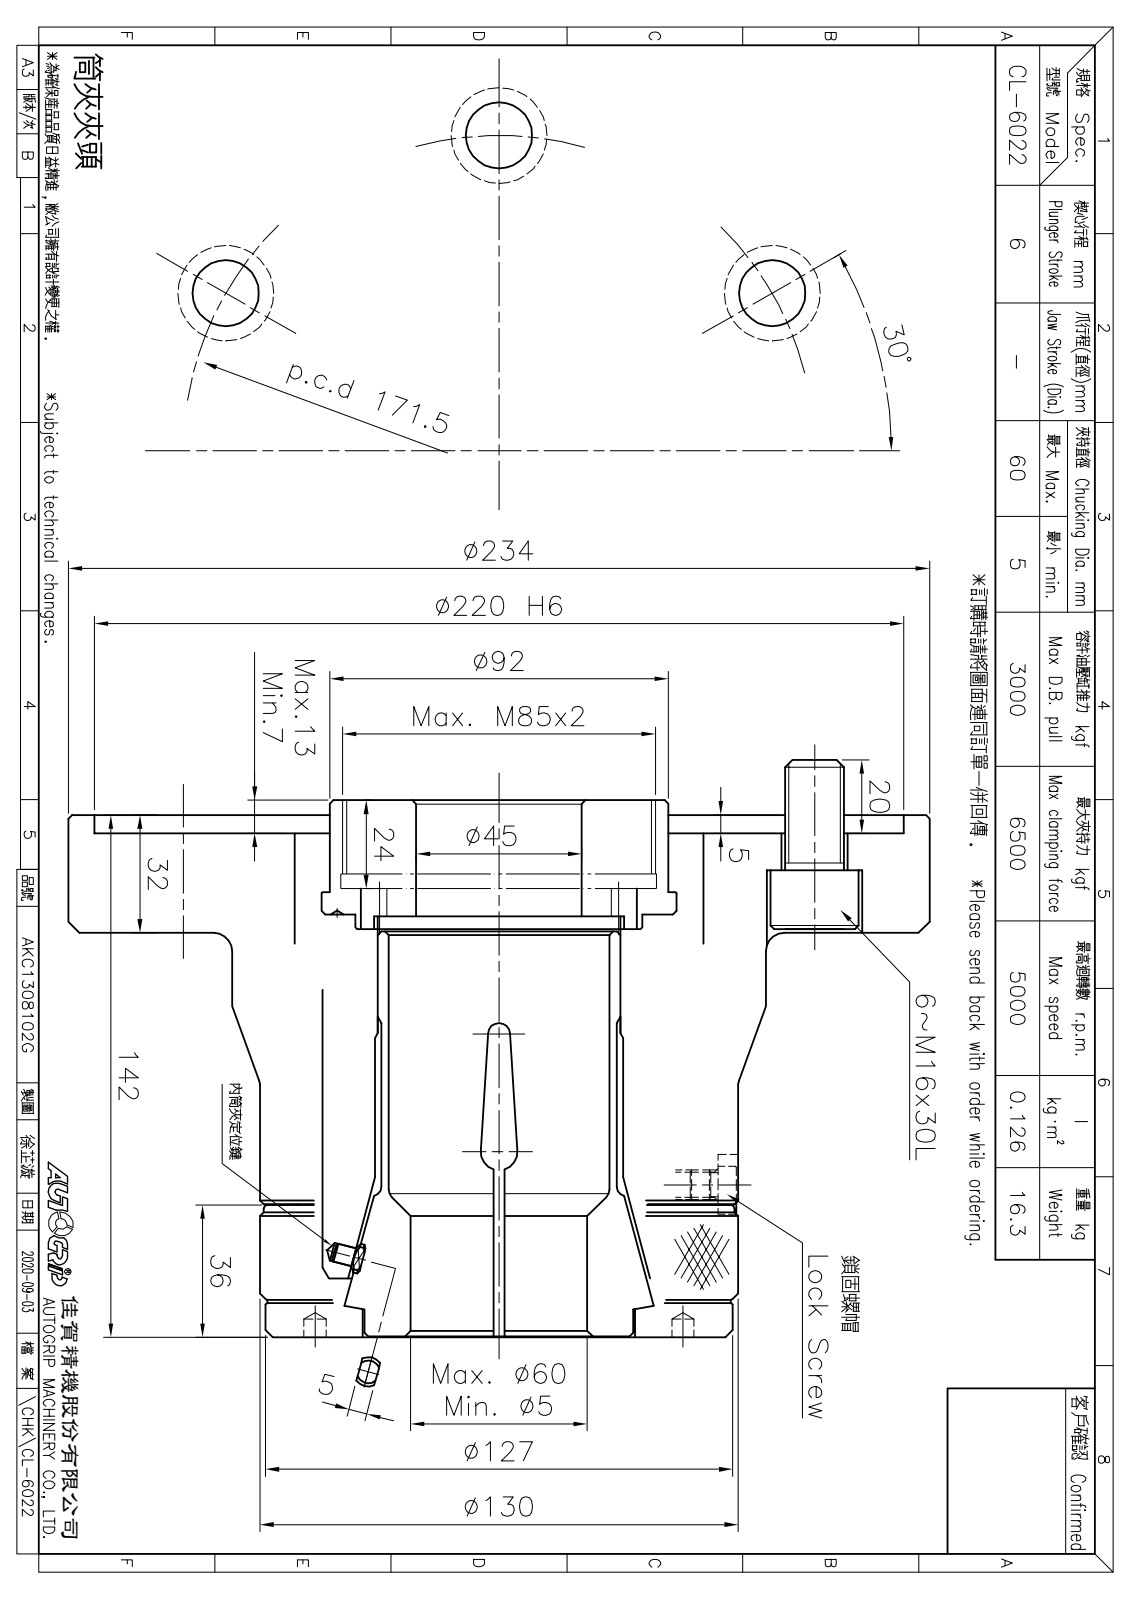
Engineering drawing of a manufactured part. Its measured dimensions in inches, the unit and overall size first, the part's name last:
Units: inches
Overall size (bounding box): 9.213 × 9.213 × 6.173
Round holes (diameter × count): ⌀0.709 ×6, ⌀1.024 ×6, ⌀0.236 ×2, ⌀0.197 ×1, ⌀0.268 ×1, ⌀2.402 ×1, ⌀2.598 ×1, ⌀2.657 ×1, ⌀2.677 ×1, ⌀2.913 ×1, ⌀3.071 ×1, ⌀3.268 ×1
Round bosses / shafts (diameter × count): ⌀0.945 ×6, ⌀0.63 ×6, ⌀9.213 ×1, ⌀5.709 ×1, ⌀5.118 ×1, ⌀5.039 ×1, ⌀5 ×1, ⌀4.961 ×1
Partial cylindrical surfaces — rounded edges, fillets, slot ends (radius × count): R0.335 ×3, R0.157 ×1, R0.315 ×1, R0.325 ×1
Main face-to-face distances: 1.063, 0.63, 0.197, 0.315, 0.591, 0.433, 0.709, 0.354, 3.969, 3.26
Hole centre spacings: 3.376, 4.681, 5.847, 1.407, 1.969, 2.937, 2.937, 5.344
Volume: 131.1 in³ · Surface area: 541.6 in²
Bodies: 12 solids, 386 faces (148 planar, 127 cylindrical, 111 other)
Part name (STEP PRODUCT): CF-CL-6017-02000; CF-CL-6022-02020; CF-CL-6022-04010; CF-CL-42-08000 (+4 more)
STEP written by: SolidWorks 2016 (CONFIG_CONTROL_DESIGN)
